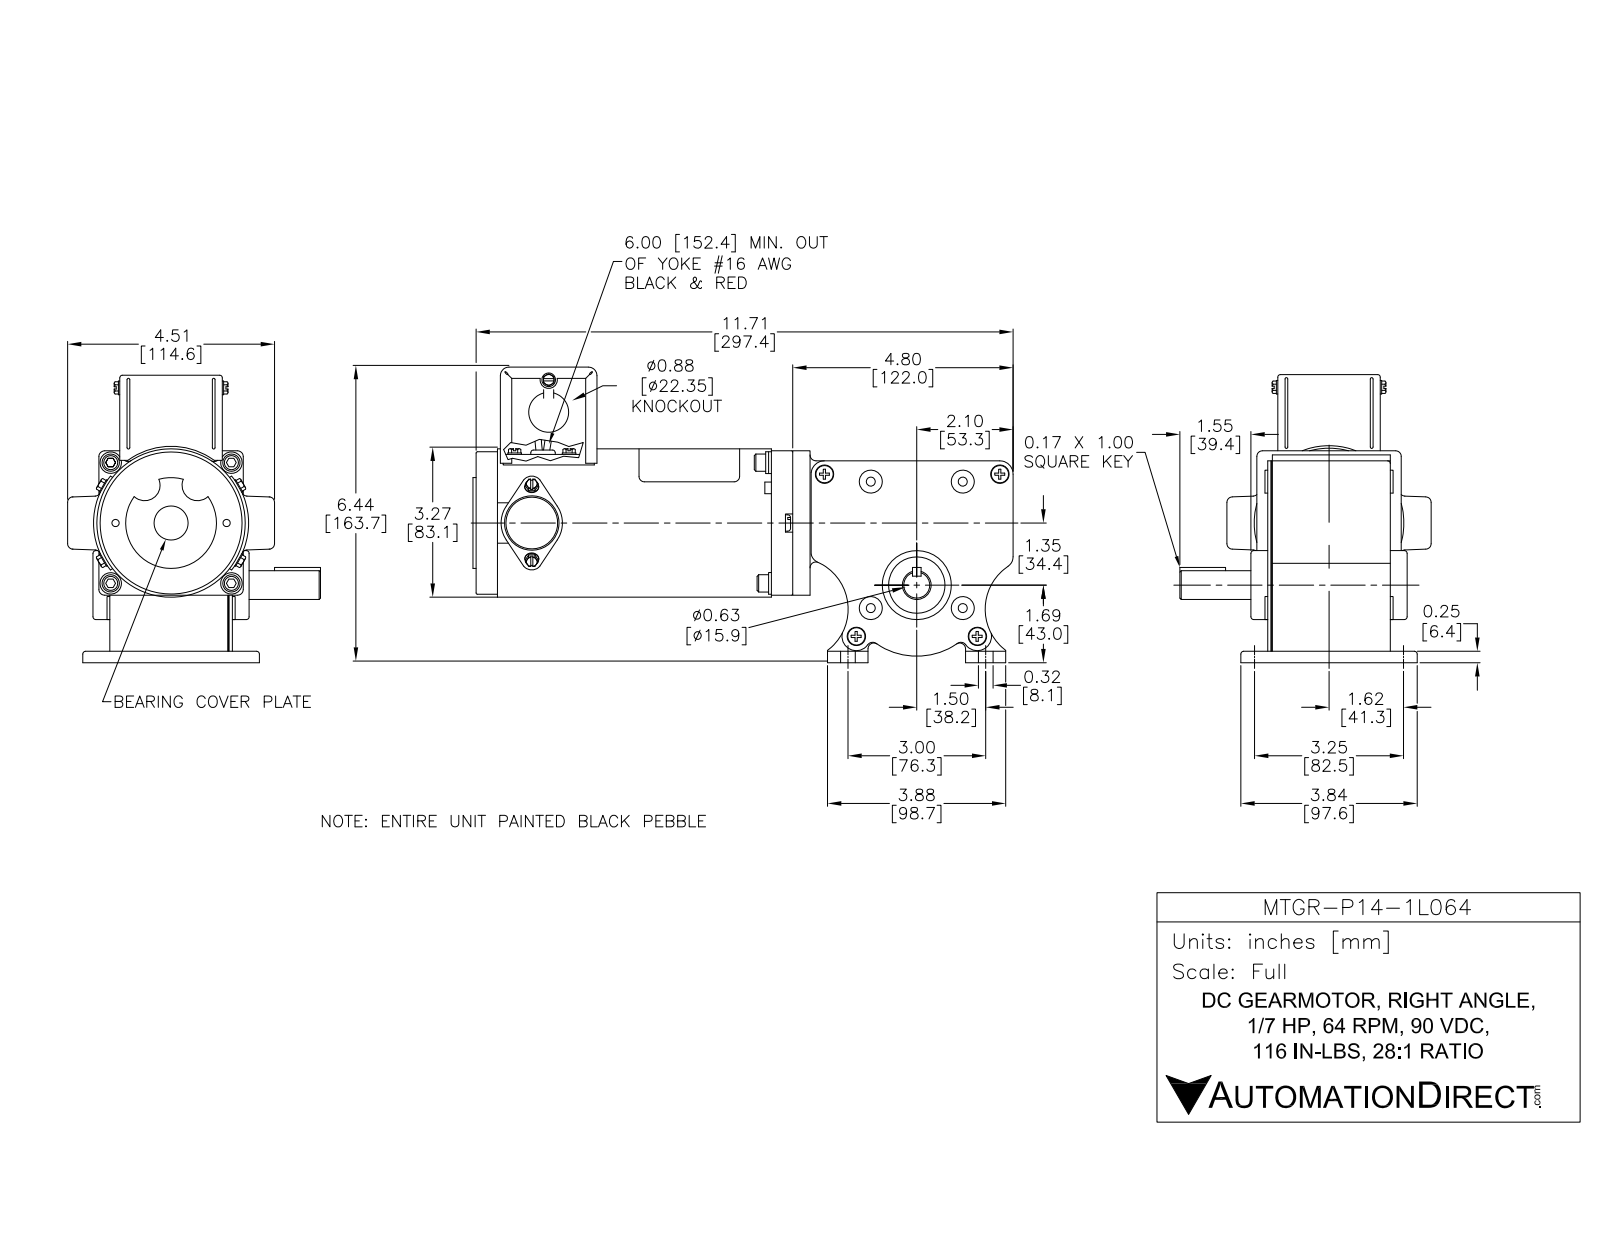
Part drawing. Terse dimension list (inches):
name: P14-1L064
written by: SolidWorks 2013 (AUTOMOTIVE_DESIGN)
unit: in
bodies: 43 solids, 797 faces (486 planar, 283 cylindrical, 28 other)
size: 11.791 × 6.522 × 5.415
volume: 64.64 in³; area: 475.7 in²
holes: 5× ⌀0.5, 4× ⌀0.125, 4× ⌀0.197, 4× ⌀0.4, 2× ⌀0.198, 1× ⌀0.25, 1× ⌀0.3, 1× ⌀0.375, 1× ⌀0.625, 1× ⌀1, 1× ⌀1.125, 1× ⌀1.5
bosses: 6× ⌀0.375, 4× ⌀0.3, 3× ⌀0.375, 2× ⌀0.125, 2× ⌀0.1, 1× ⌀3.156, 1× ⌀0.625, 1× ⌀0.301
rounds: 4× R0.125, 4× R0.16, 4× R0.191, 4× R0.234, 4× R0.25, 2× R0.13, 2× R0.159, 2× R0.29
face distances: 0.015, 0.03, 0.031, 2.603, 2.588, 2.573, 0.1, 0.07, 0.085, 2.673
hole spacings: 1.318, 1.859, 2.63, 2.865, 1.118, 1.23, 2, 2.37
